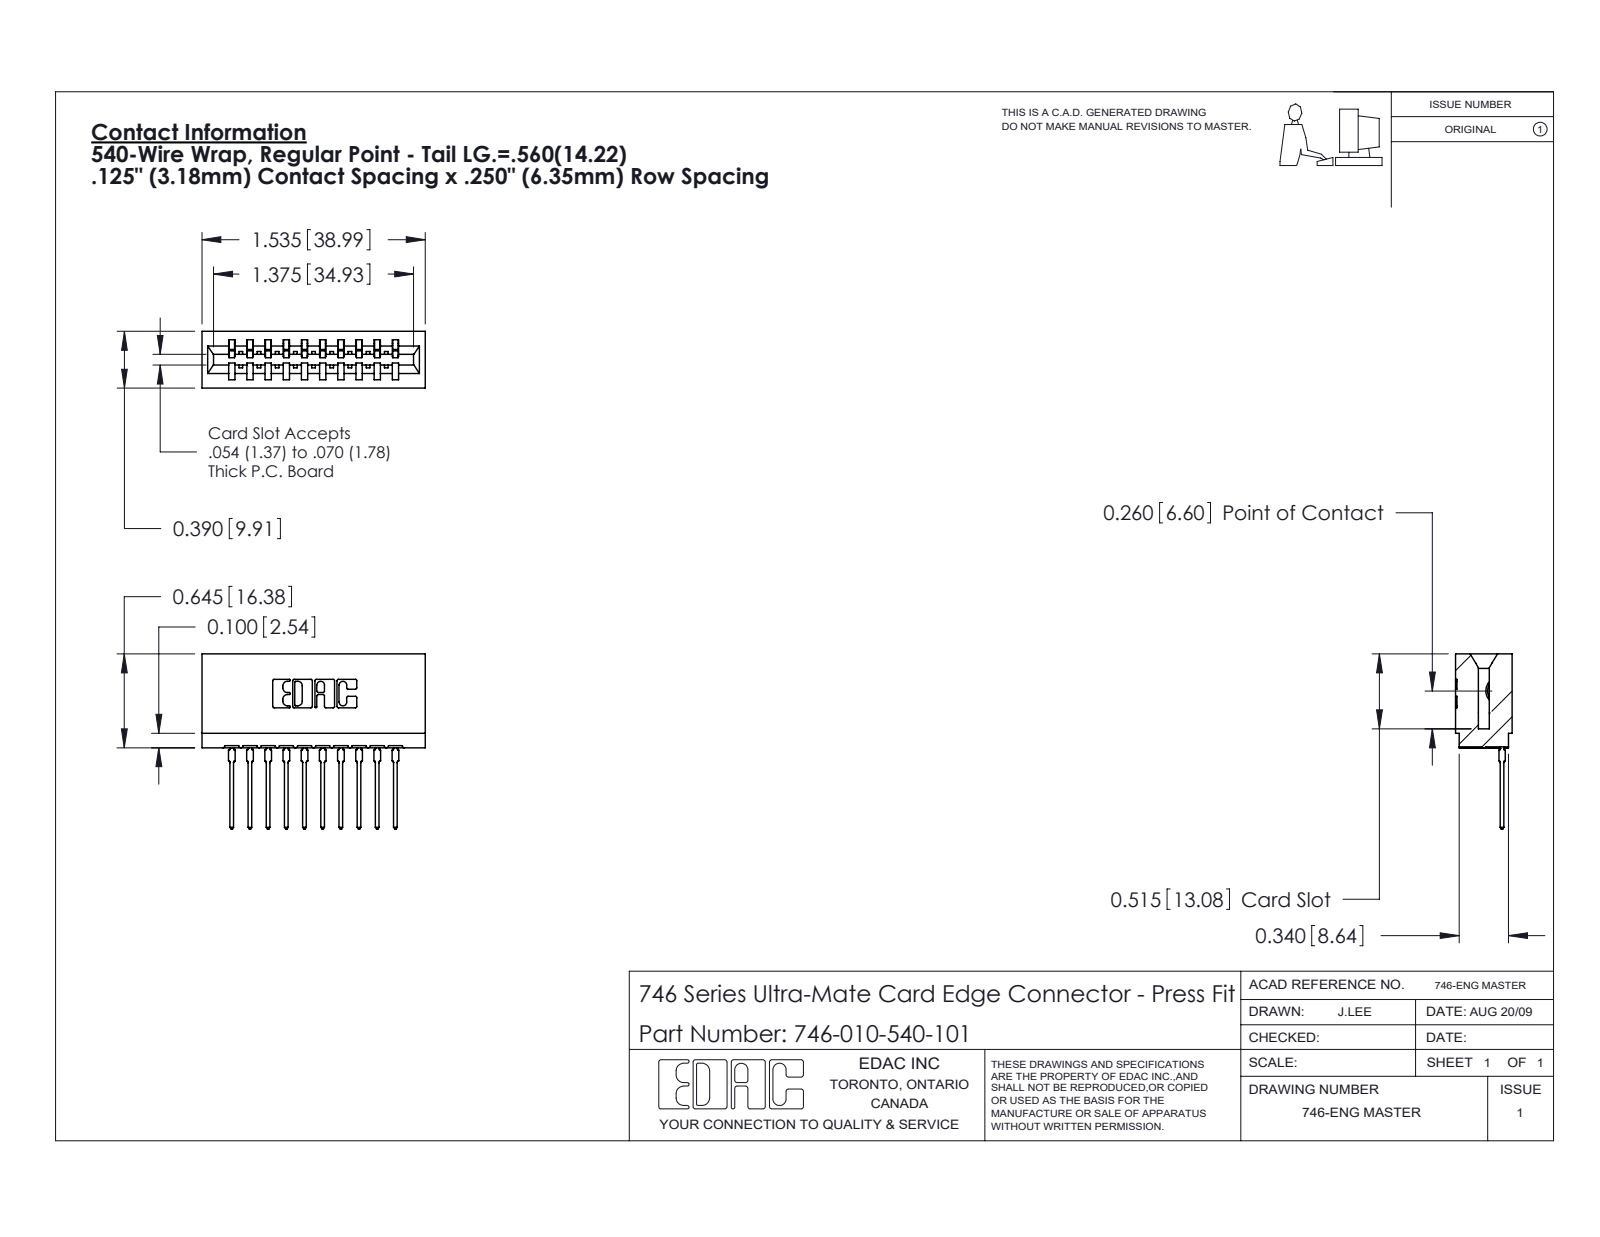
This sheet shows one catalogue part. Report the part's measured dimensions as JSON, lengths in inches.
{"part_name": "746-010-540-101; 746-292-001_540; 746 Part_.515 Slot Depth - 01", "step_written_by": "SolidWorks 2020 (CONFIG_CONTROL_DESIGN)", "units": "inches", "bodies": {"solids": 11, "faces": 1177, "planar": 685, "cylindrical": 232, "other": 260}, "overall_size": [1.535, 1.204, 0.39], "volume_in3": 0.263, "surface_area_in2": 9.268, "partial_cylinders_radius": [[0.01, 22], [0.021, 20], [0.015, 11], [0.007, 6], [0.031, 6], [0.005, 4], [0.011, 4], [0.026, 3]], "face_to_face_distances": [0.25, 0.5, 0.333, 0.057, 0.125, 0.042, 0.375, 0.208, 0.125, 0.39]}
